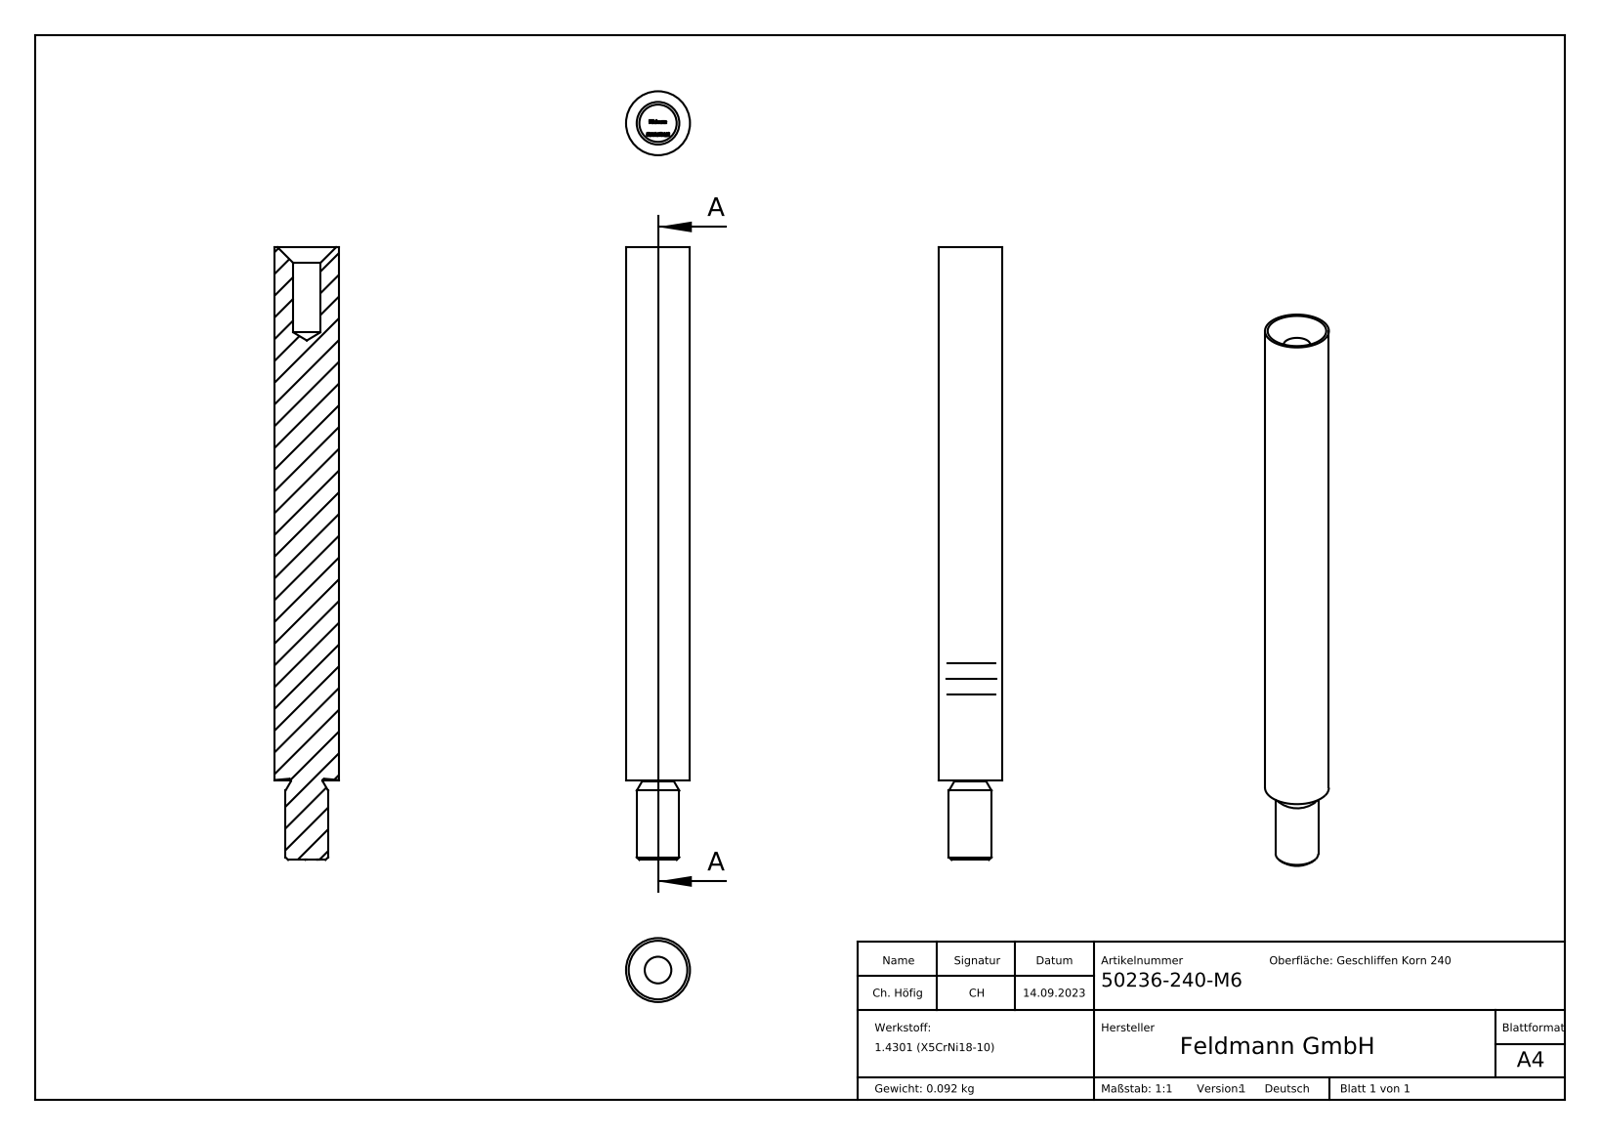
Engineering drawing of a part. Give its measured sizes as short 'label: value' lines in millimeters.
name: 50236-240-M6
written by: SolidWorks 2018 (CONFIG_CONTROL_DESIGN)
unit: mm
bodies: 1 solid, 269 faces (157 planar, 3 cylindrical, 109 other)
size: 115 × 12 × 12
volume: 11 602 mm³; area: 4 632 mm²
holes: 1× ⌀5
bosses: 1× ⌀12, 1× ⌀8
face distances: 115, 114.9, 0.77, 1.29, 2.38, 2.39, 0.72, 1.55, 2.44, 0.57
